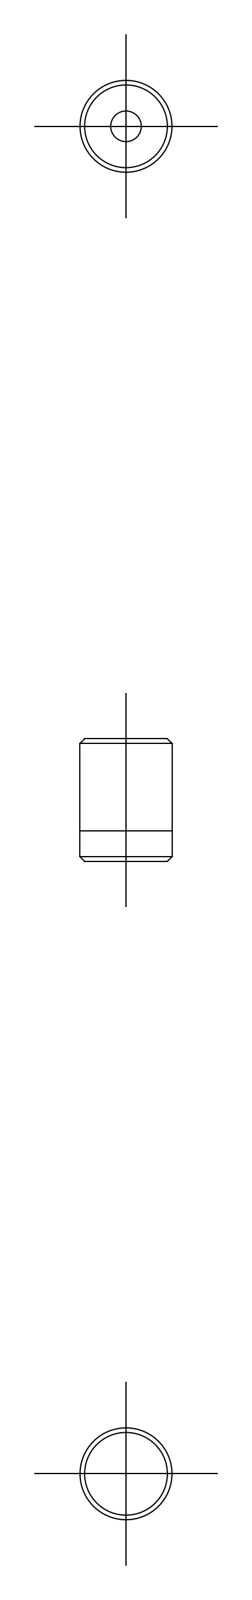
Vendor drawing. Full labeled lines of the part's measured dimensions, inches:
STEP written by: CADfix (AUTOMOTIVE_DESIGN)
Units: inches
Bodies: 1 solid, 16 faces (0 planar, 0 cylindrical, 16 other)
Overall size (bounding box): 0.315 × 0.236 × 0.236
Volume: 0.014 in³ · Surface area: 0.33 in²
